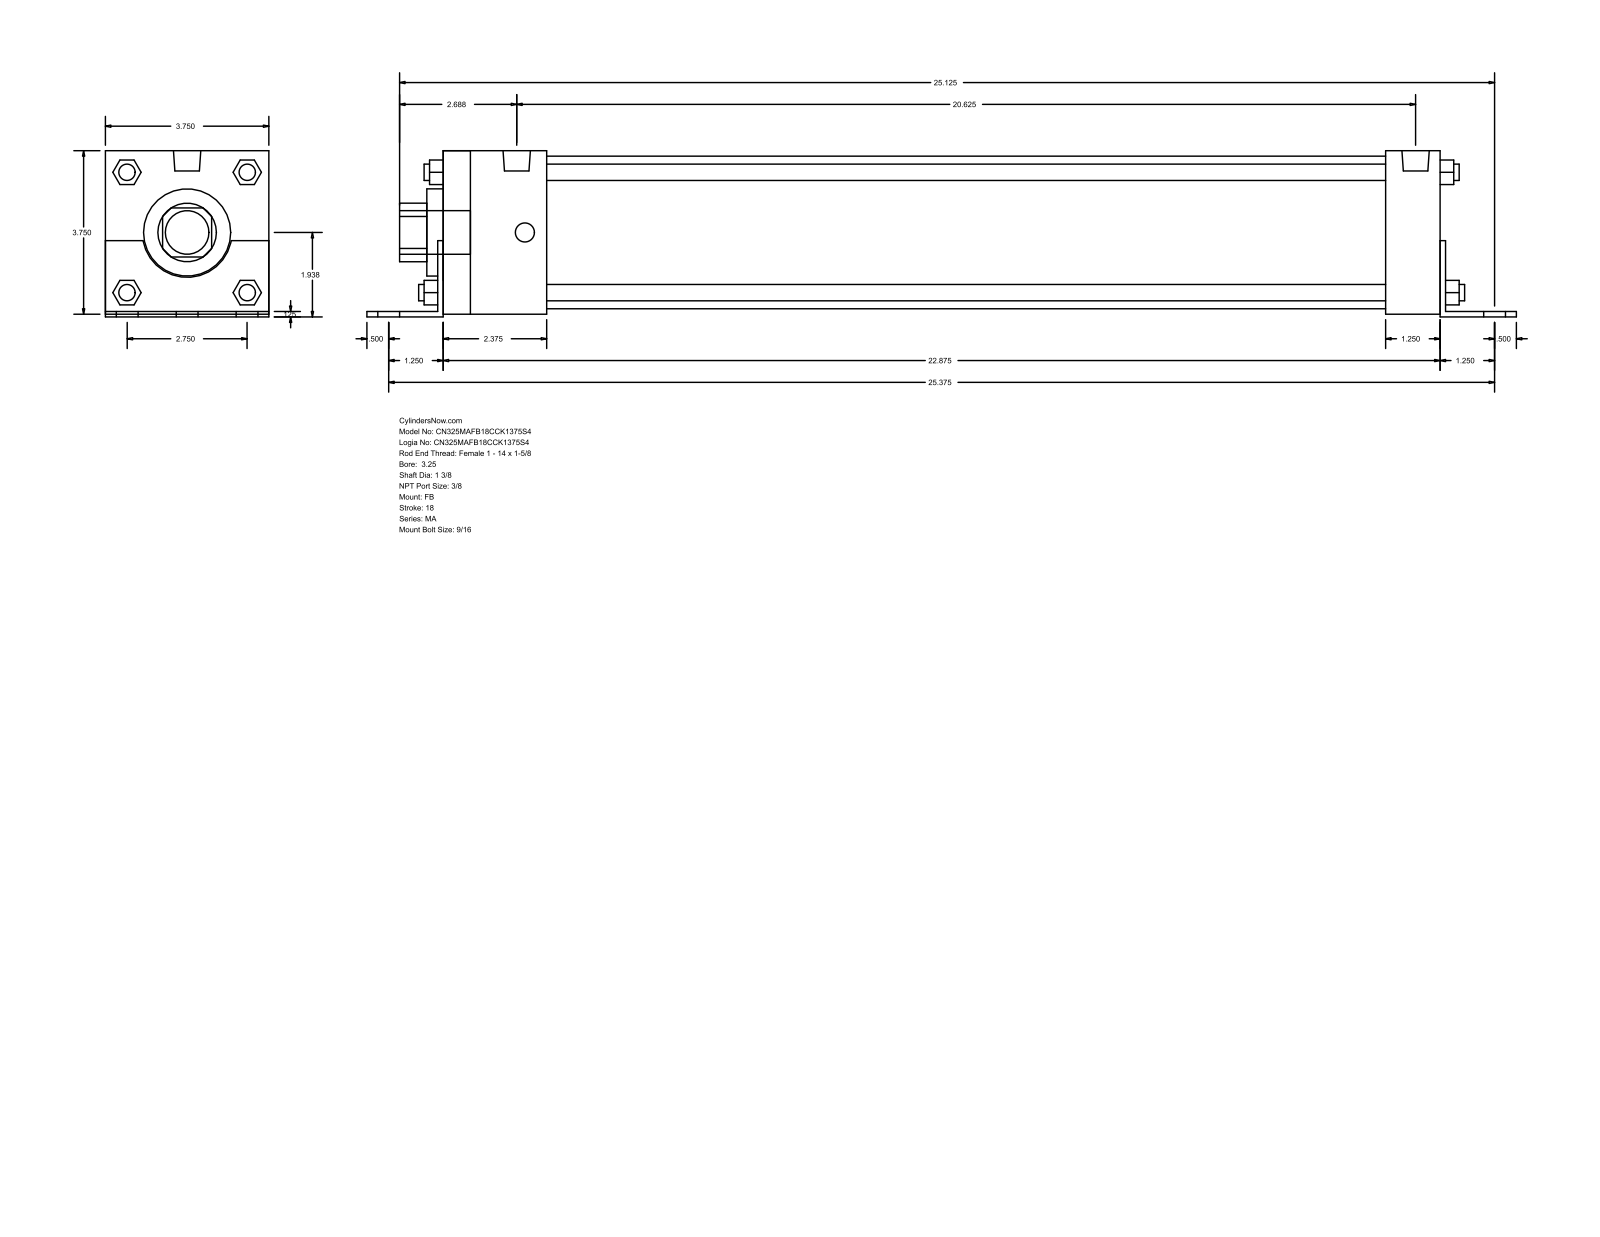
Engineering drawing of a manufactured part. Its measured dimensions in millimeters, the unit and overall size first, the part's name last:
Units: millimetres
Overall size (bounding box): 669.92 × 96.84 × 95.25
Round holes (diameter × count): ⌀34.92 ×1, ⌀50.8 ×1, ⌀88.9 ×1
Round bosses / shafts (diameter × count): ⌀14.29 ×6, ⌀11.11 ×4, ⌀9.53 ×4, ⌀15.93 ×2, ⌀25.4 ×1
Partial cylindrical surfaces — rounded edges, fillets, slot ends (radius × count): R17.06 ×1, R26.16 ×1
Main face-to-face distances: 95.24, 3.17, 1.59, 96.83, 1.58, 93.66, 3.18, 581.02, 584.2, 31.75
Bodies: 0 solids, 140 faces (105 planar, 35 cylindrical, 0 other)
Part name (STEP PRODUCT): MA_FB__0325_1.375
STEP written by: GSSL Pune (CONFIG_CONTROL_DESIGN)
